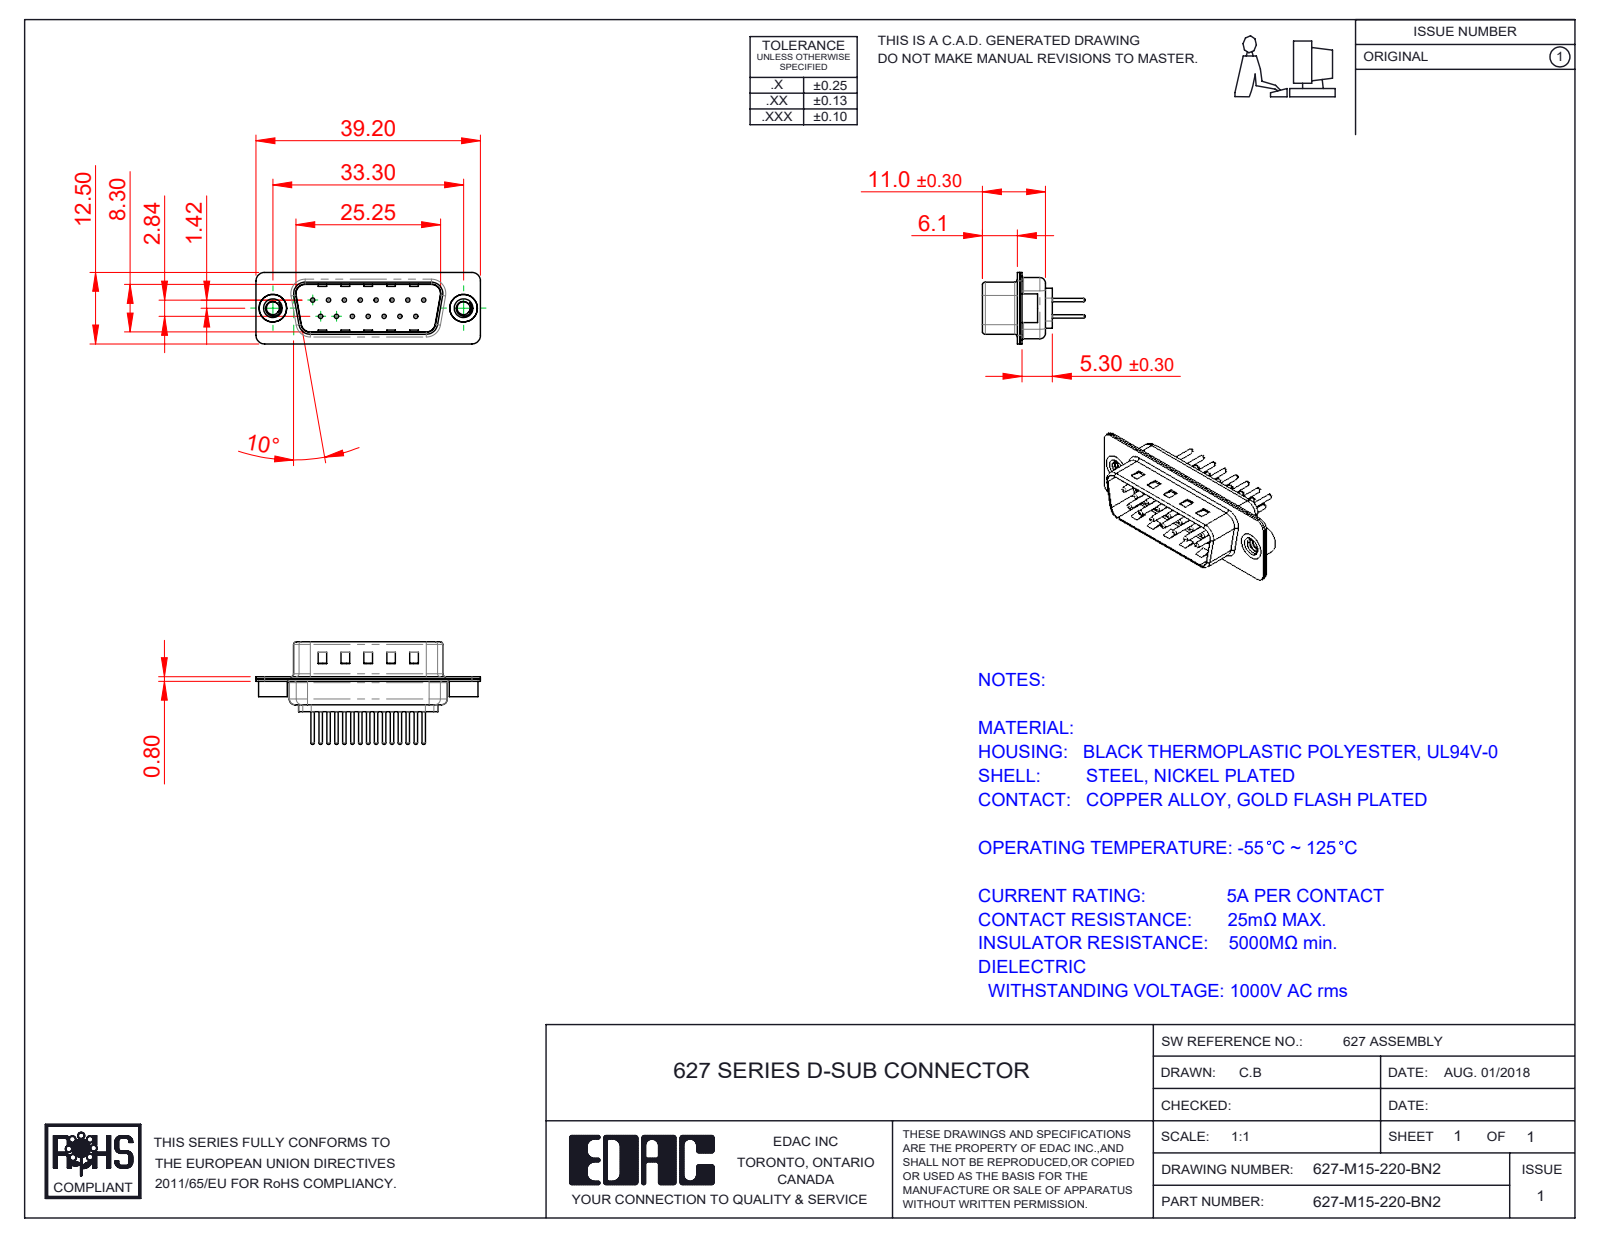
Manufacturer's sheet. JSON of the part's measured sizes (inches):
{"part_name": "627M Shell Rear_15 Contacts; 627M Contact Row 2_20; 627-M15-220-BN2; 627M 4-40 Threaded Rivet (+3 more)", "step_written_by": "SolidWorks 2020 (CONFIG_CONTROL_DESIGN)", "units": "inches", "bodies": {"solids": 20, "faces": 895, "planar": 244, "cylindrical": 343, "other": 308}, "overall_size": [1.543, 0.705, 0.492], "volume_in3": 0.112, "surface_area_in2": 7.452, "round_holes": [[0.03, 15], [0.063, 15], [0.079, 15], [0.089, 2], [0.157, 2], [0.189, 2]], "round_bosses_or_shafts": [[0.059, 15], [0.024, 15], [0.197, 2], [0.193, 2]], "partial_cylinders_radius": [[0.059, 16], [0.079, 12], [0.02, 8], [0.063, 8], [0.01, 4], [0.024, 4], [0.026, 4], [0.035, 4]], "face_to_face_distances": [0.016, 0.031, 0.374, 0.358, 0.343, 0.39, 0.047, 0.24, 0.224, 0.209], "hole_center_spacings": [0.124, 0.109, 0.218, 0.327, 0.436, 0.198, 0.198, 0.294]}
